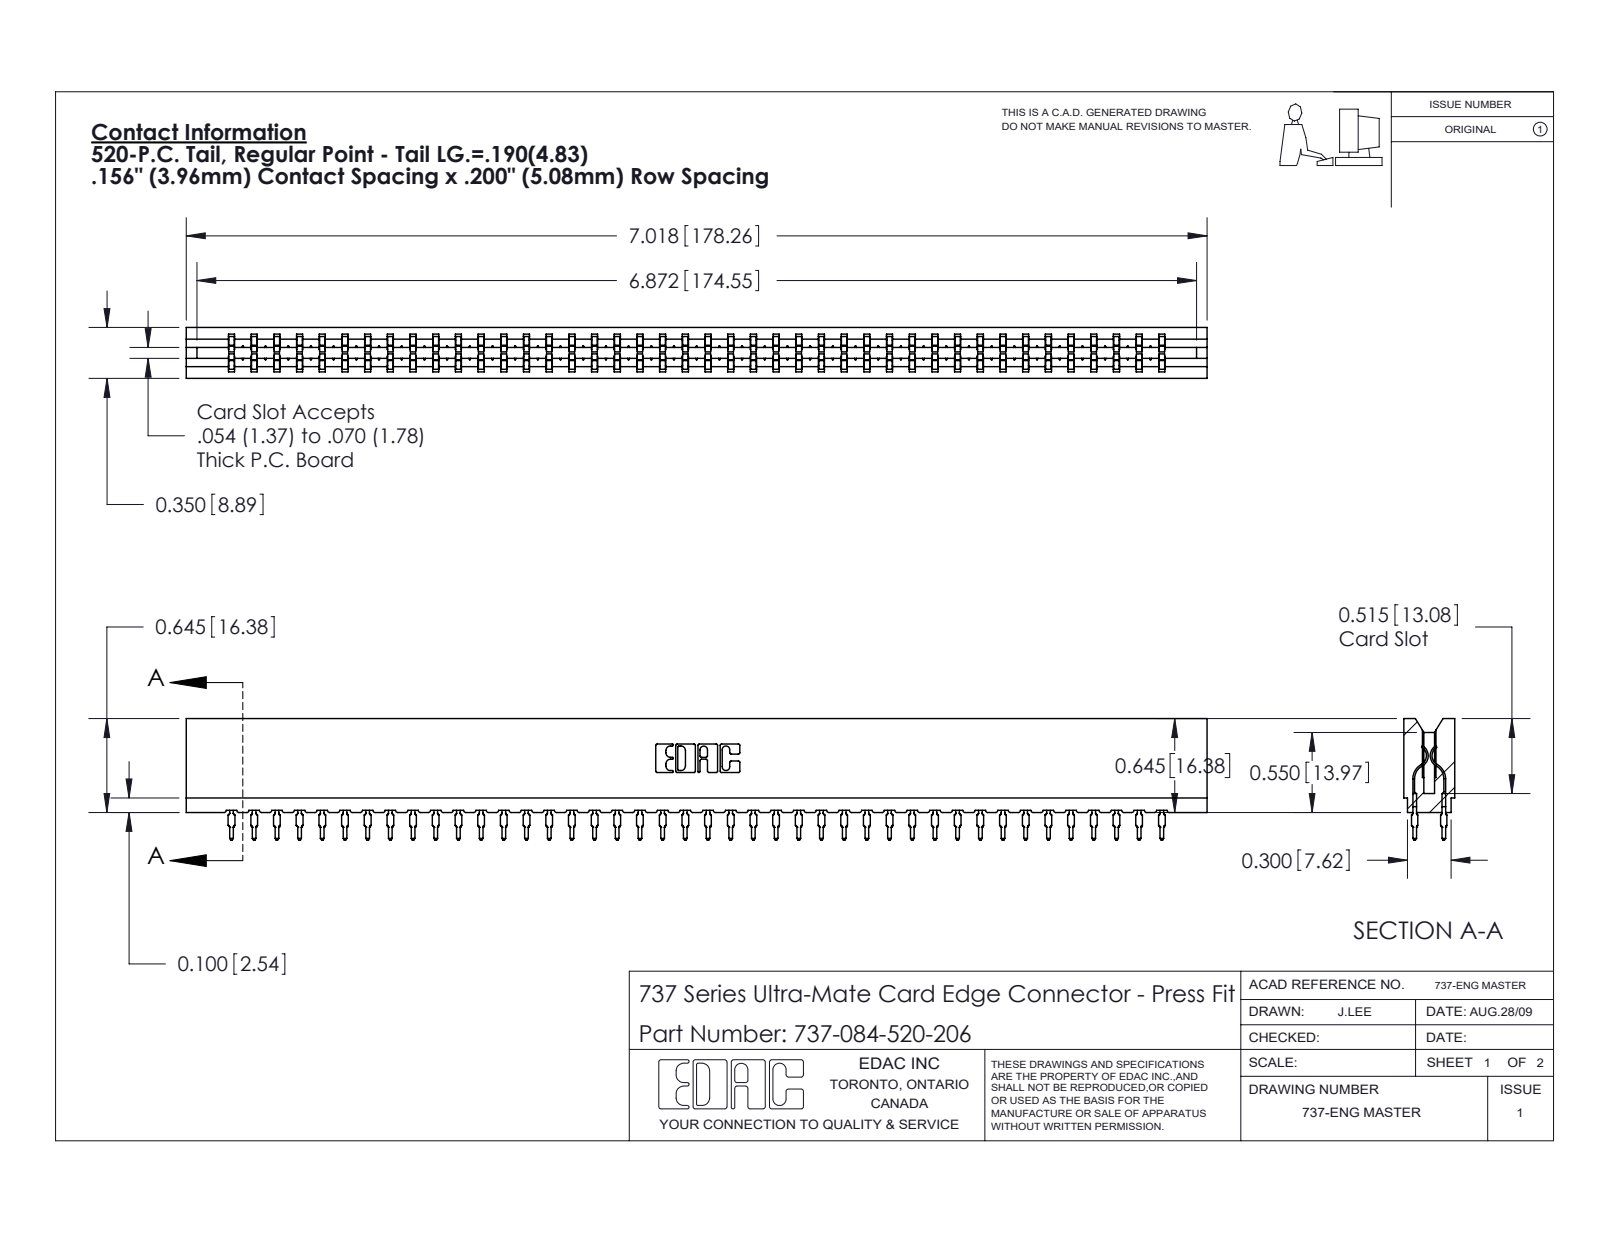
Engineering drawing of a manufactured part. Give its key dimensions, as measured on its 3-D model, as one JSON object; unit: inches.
{"part_name": "745-292-001_520; 737 Part_Insulator Option - 06; 737-084-520-206", "step_written_by": "SolidWorks 2020 (CONFIG_CONTROL_DESIGN)", "units": "inches", "bodies": {"solids": 85, "faces": 7655, "planar": 3961, "cylindrical": 1510, "other": 2184}, "overall_size": [7.018, 0.836, 0.35], "volume_in3": 1.07, "surface_area_in2": 38.82, "partial_cylinders_radius": [[0.021, 168], [0.015, 84], [0.01, 22], [0.005, 8], [0.011, 8], [0.007, 6], [0.031, 6], [0.026, 3]], "face_to_face_distances": [0.138, 0.212, 0.35, 0.074, 0.063, 0.287, 0.076, 0.149, 0.045, 0.305]}
